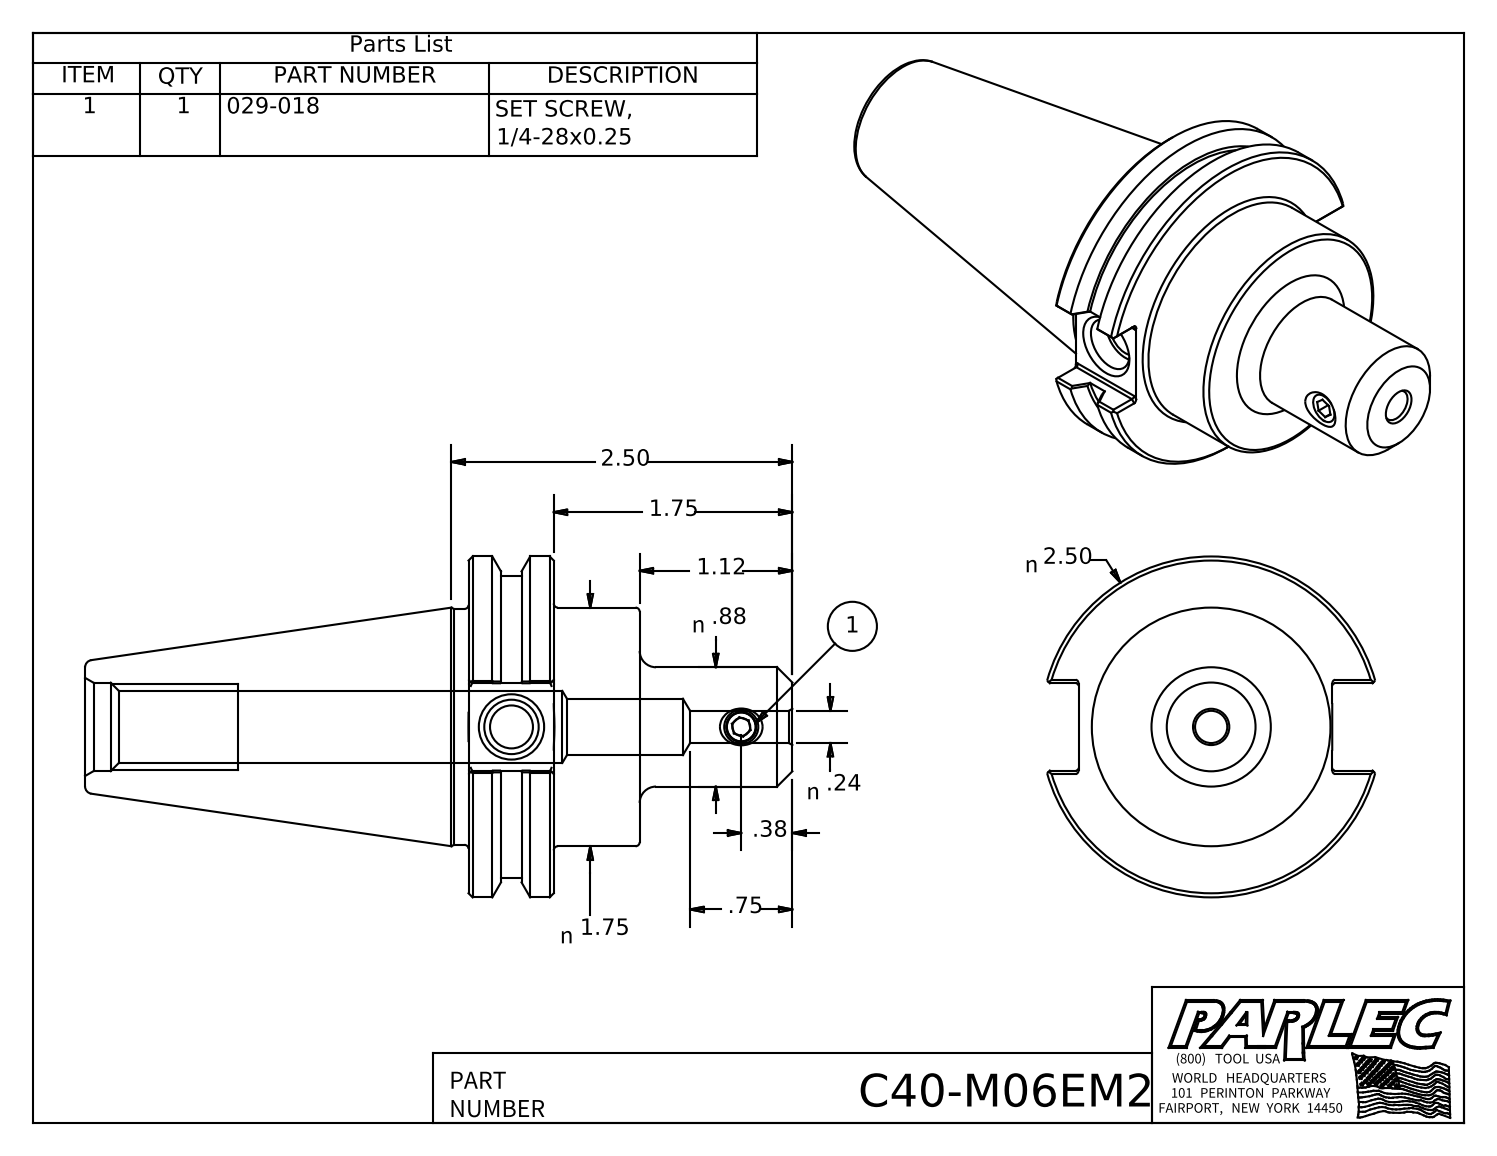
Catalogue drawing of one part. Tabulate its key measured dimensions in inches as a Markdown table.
| quantity | value |
| --- | --- |
| part name | C40-M06EM2; 029-018 |
| STEP written by | Autodesk Inventor 2012 (AUTOMOTIVE_DESIGN) |
| units | inches |
| bodies | 2 solids, 104 faces (41 planar, 29 cylindrical, 34 other) |
| overall size | 5.187 × 2.5 × 2.406 |
| volume | 8.131 in³ |
| surface area | 39.93 in² |
| round holes (diameter × count) | 0.211 × 1, 0.236 × 1, 0.315 × 1, 0.399 × 1, 0.413 × 1, 0.527 × 1, 0.648 × 1 |
| round bosses / shafts (diameter × count) | 2.5 × 1, 2.219 × 1, 1.75 × 1, 1.73 × 1, 0.875 × 1, 0.25 × 1 |
| partial cylindrical surfaces (radius × count) | 0.02 × 12 |
| main face-to-face distances | 0.625, 1.255, 0.63, 2.375, 1.75, 1.12, 0.64, 1.86, 2.812, 3.437 |
| hole center spacings | 1.685 |
